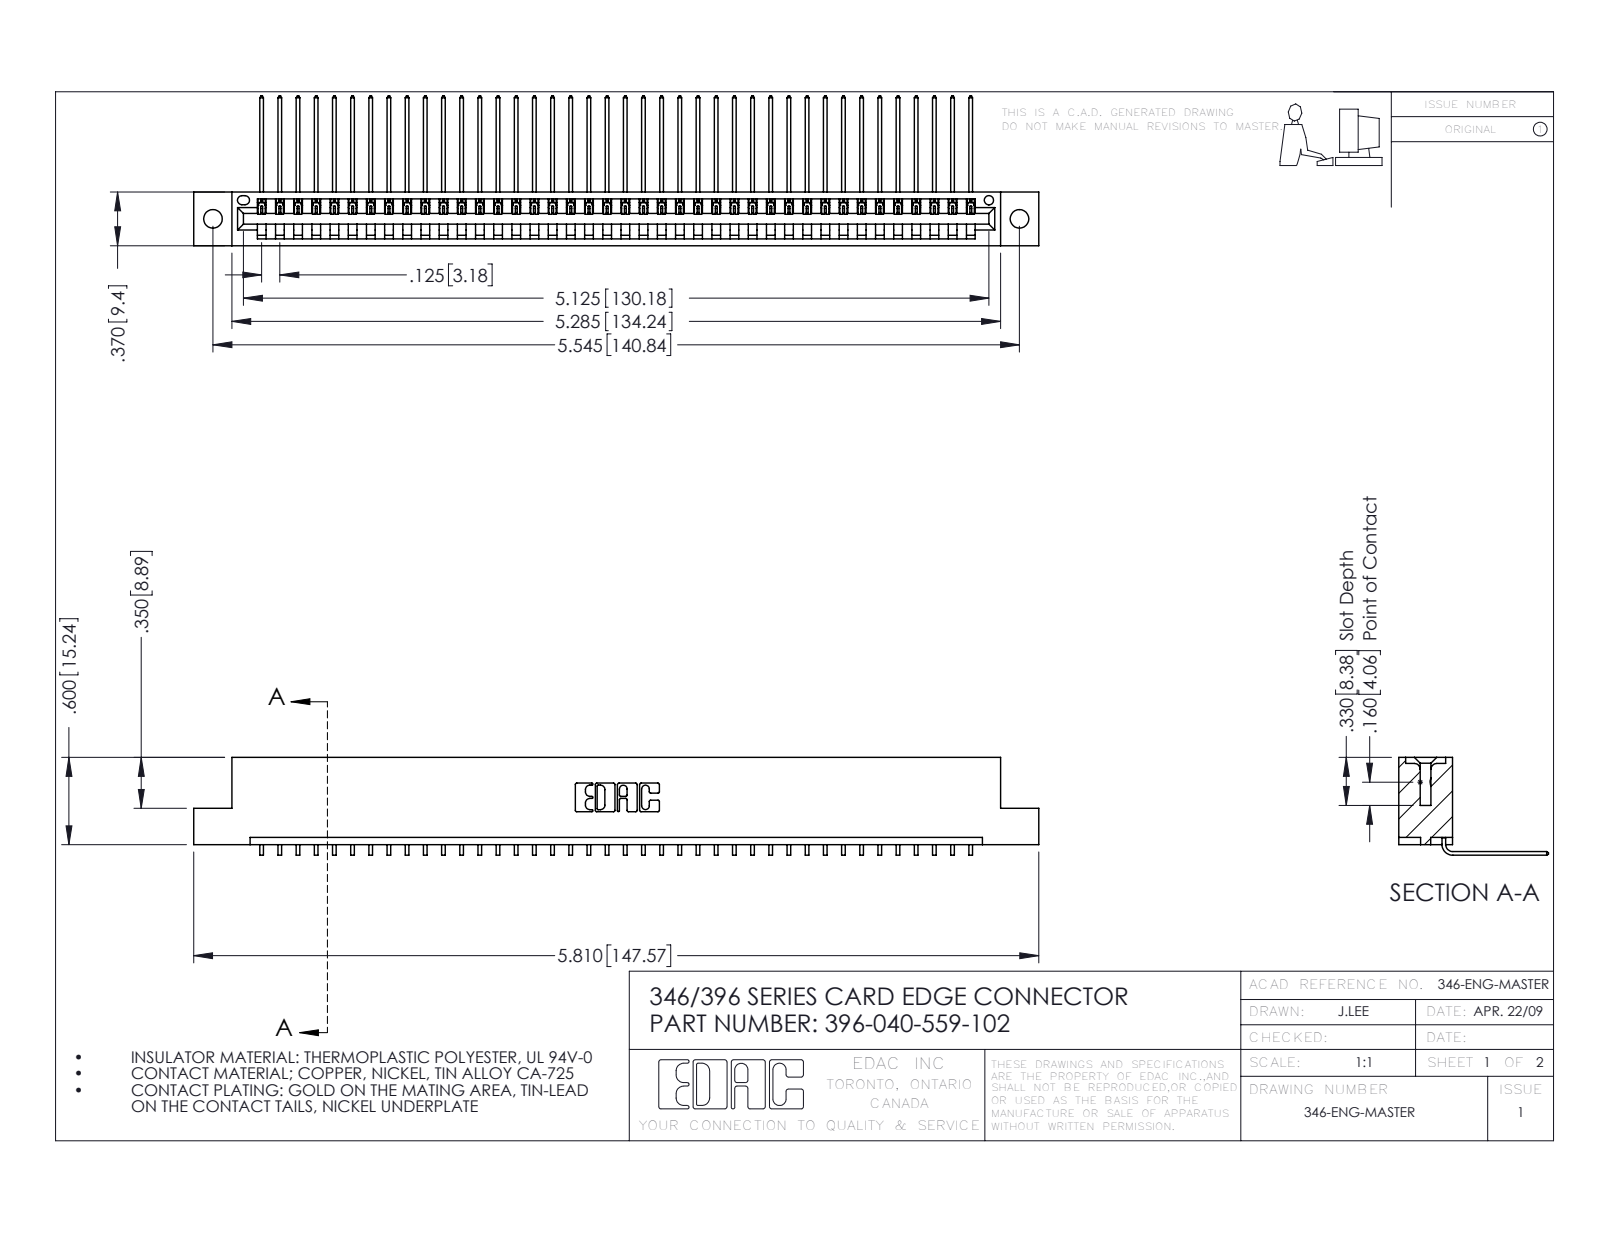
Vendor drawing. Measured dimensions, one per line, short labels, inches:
name: 345-292-001_558 559 Tail - 1; 346 Part_Flush Mounting Lugs - 0.128 Dia; 396-040-559-102
written by: SolidWorks 2016 (CONFIG_CONTROL_DESIGN)
unit: in
bodies: 41 solids, 2522 faces (1756 planar, 766 cylindrical, 0 other)
size: 5.81 × 1.03 × 0.673
volume: 0.867 in³; area: 28.31 in²
holes: 2× ⌀0.128, 1× ⌀0.064
rounds: 80× R0.006, 22× R0.01, 6× R0.007, 6× R0.031, 3× R0.026, 2× R0.031, 2× R0.04, 1× R0.014
face distances: 0.048, 0.322, 0.37, 0.25, 0.025, 0.072, 0.298, 0.148, 0.222, 0.1
hole spacings: 0.246, 5.336, 5.545
